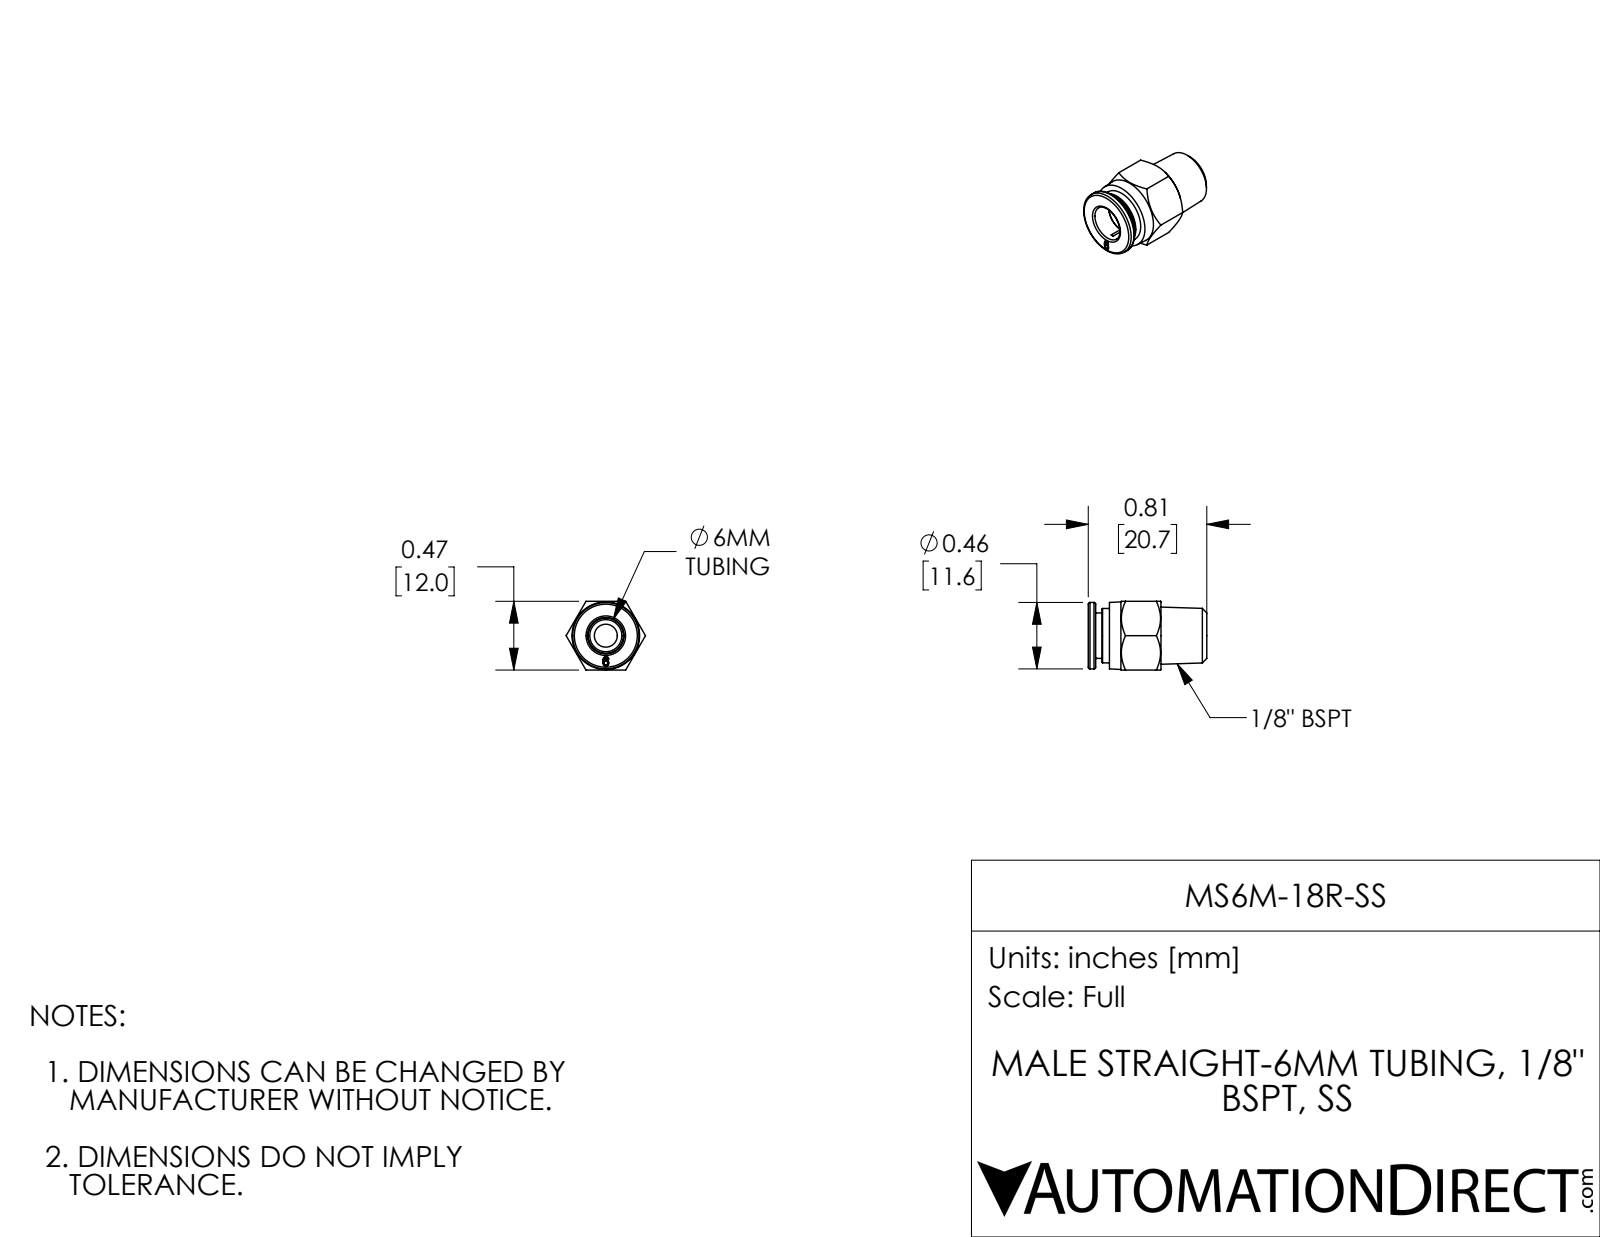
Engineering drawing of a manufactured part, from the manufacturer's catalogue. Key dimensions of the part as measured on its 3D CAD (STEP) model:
Part name (STEP PRODUCT): MS6M-18R-SS
STEP written by: SolidWorks 2017 (AUTOMOTIVE_DESIGN)
Units: inches
Bodies: 1 solid, 77 faces (23 planar, 14 cylindrical, 40 other)
Overall size (bounding box): 0.815 × 0.546 × 0.472
Volume: 0.085 in³ · Surface area: 2.215 in²
Round holes (diameter × count): ⌀0.157 ×1, ⌀0.244 ×1, ⌀0.248 ×1, ⌀0.319 ×1
Round bosses / shafts (diameter × count): ⌀0.457 ×1, ⌀0.374 ×1, ⌀0.313 ×1
Main face-to-face distances: 0.472, 0.051, 0.094, 0.146, 0.354, 0.449, 0.5, 0.315, 0.669, 0.764
